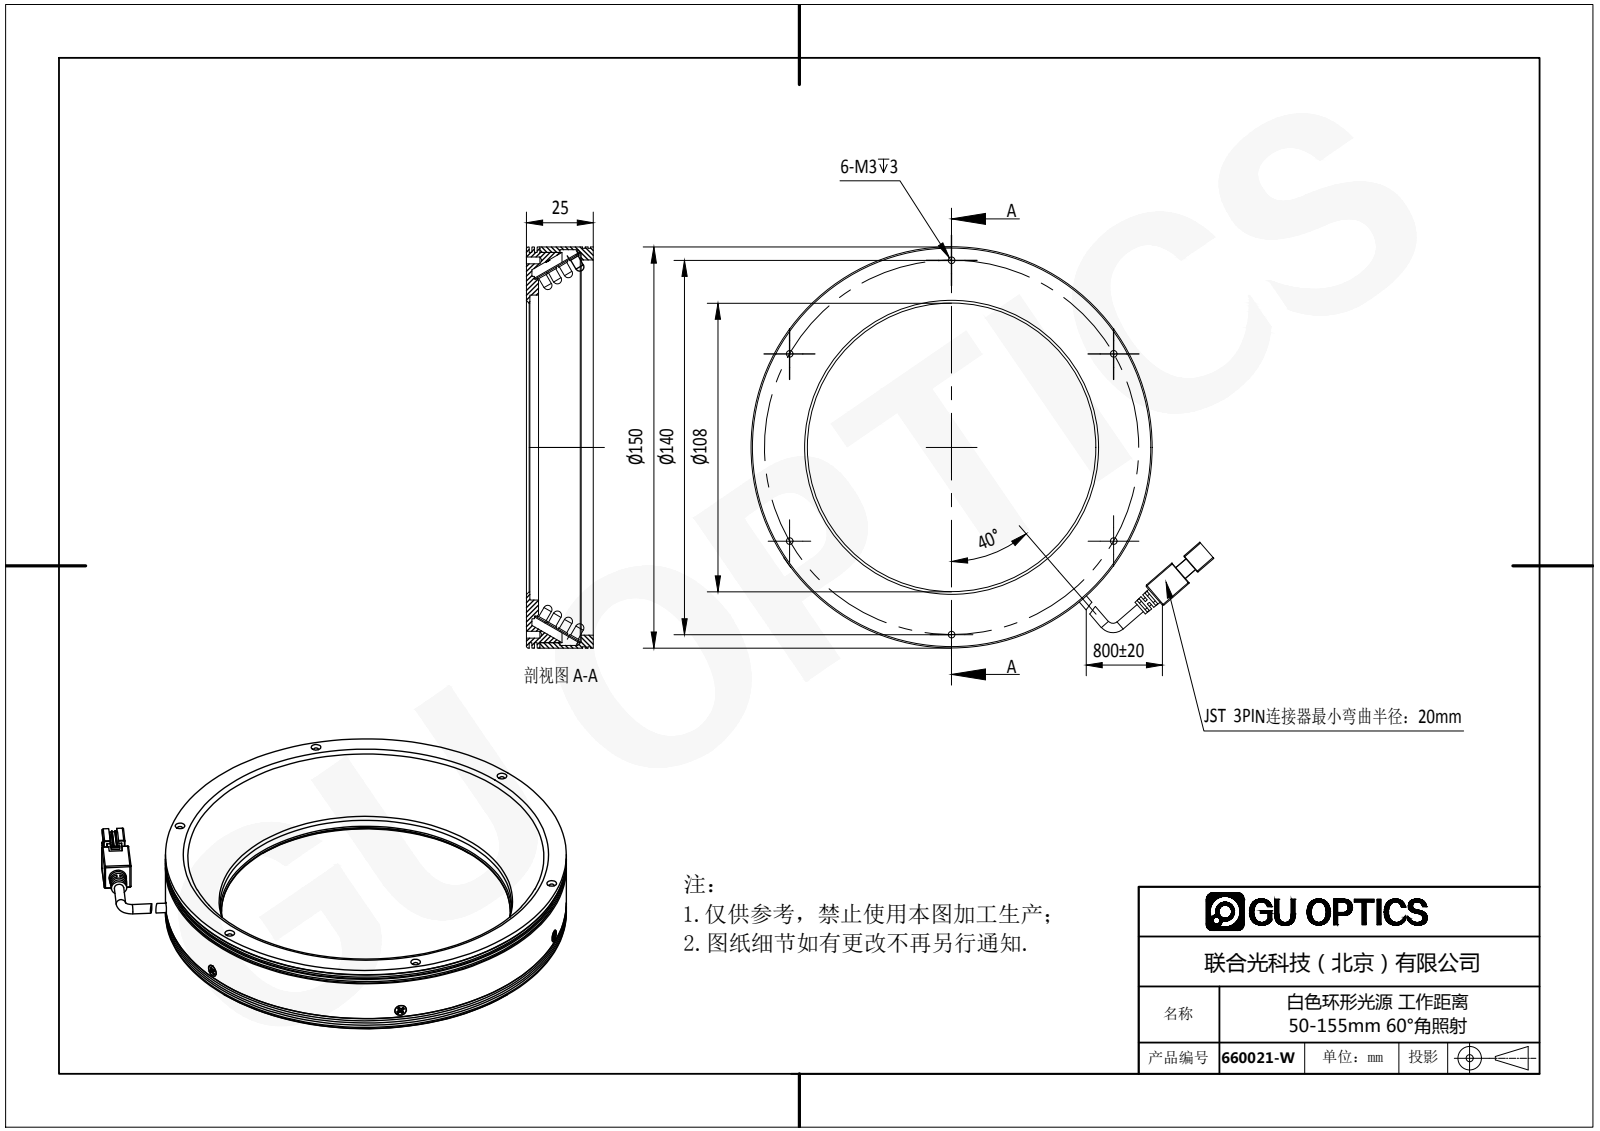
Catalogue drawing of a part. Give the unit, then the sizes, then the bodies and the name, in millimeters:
Units: millimetres
Overall size (bounding box): 173.15 × 150 × 27.1
Round holes (diameter × count): ⌀1.25 ×6, ⌀1.6 ×6, ⌀1.8 ×6, ⌀2.5 ×6, ⌀2.4 ×3, ⌀3.5 ×1, ⌀108 ×1, ⌀109 ×1, ⌀114 ×1, ⌀140.4 ×1, ⌀148 ×1
Round bosses / shafts (diameter × count): ⌀4 ×372, ⌀3 ×372, ⌀2.2 ×6, ⌀2 ×6, ⌀1.4 ×6, ⌀3.5 ×2, ⌀150 ×1, ⌀149 ×1
Partial cylindrical surfaces — rounded edges, fillets, slot ends (radius × count): R0.2 ×157, R0.1 ×15, R0.4 ×12, R0.3 ×1, R0.68 ×1, R1.4 ×1, R1.65 ×1, R7.89 ×1
Main face-to-face distances: 2, 0.5, 1, 3, 25.1, 20.49, 22.1, 4.5, 27.1, 19.99
Hole centre spacings: 72, 122.98, 124.71, 70, 71.02, 2, 72.01, 125.96
Volume: 107 139 mm³ · Surface area: 134 208 mm²
Bodies: 391 solids, 7206 faces (4800 planar, 1855 cylindrical, 551 other)
Part name (STEP PRODUCT): 660021-W
STEP written by: SolidWorks 2016 (AUTOMOTIVE_DESIGN)
